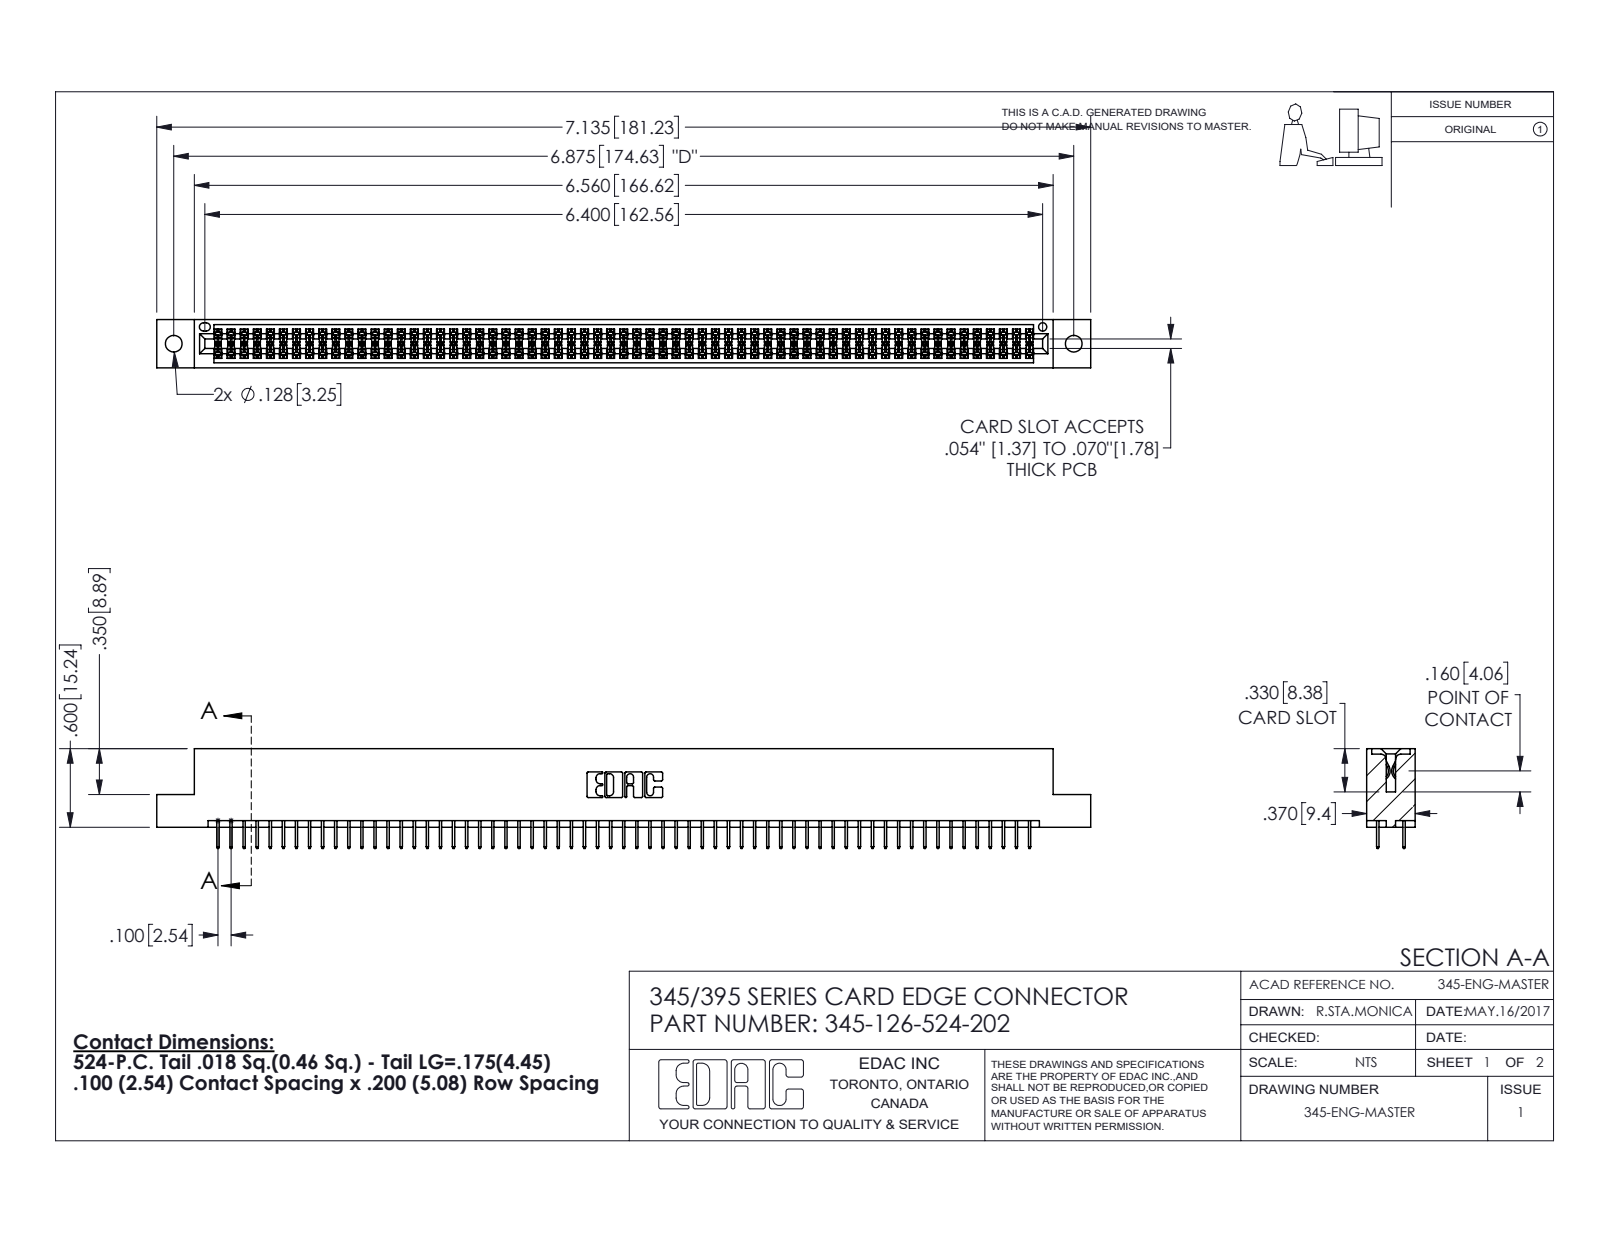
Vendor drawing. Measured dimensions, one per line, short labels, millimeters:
name: 345 Part_Flush Mounting Lugs - 0.128 Dia; 345-126-524-202; 345-292-001_345-293-124
written by: SolidWorks 2016 (CONFIG_CONTROL_DESIGN)
unit: mm
bodies: 127 solids, 6930 faces (4994 planar, 1936 cylindrical, 0 other)
size: 181.2 × 19.4 × 9.4
volume: 17 570 mm³; area: 25 610 mm²
holes: 2× ⌀3.3, 1× ⌀1.6
rounds: 189× R0.2, 22× R0.3, 6× R0.2, 6× R0.8, 3× R0.7, 2× R0.4, 2× R0.5, 2× R0.6
face distances: 1.8, 7.6, 5.1, 9.4, 2.5, 6.9, 0.6, 5.7, 1.8, 4.4
hole spacings: 6.9, 168.6, 174.6
